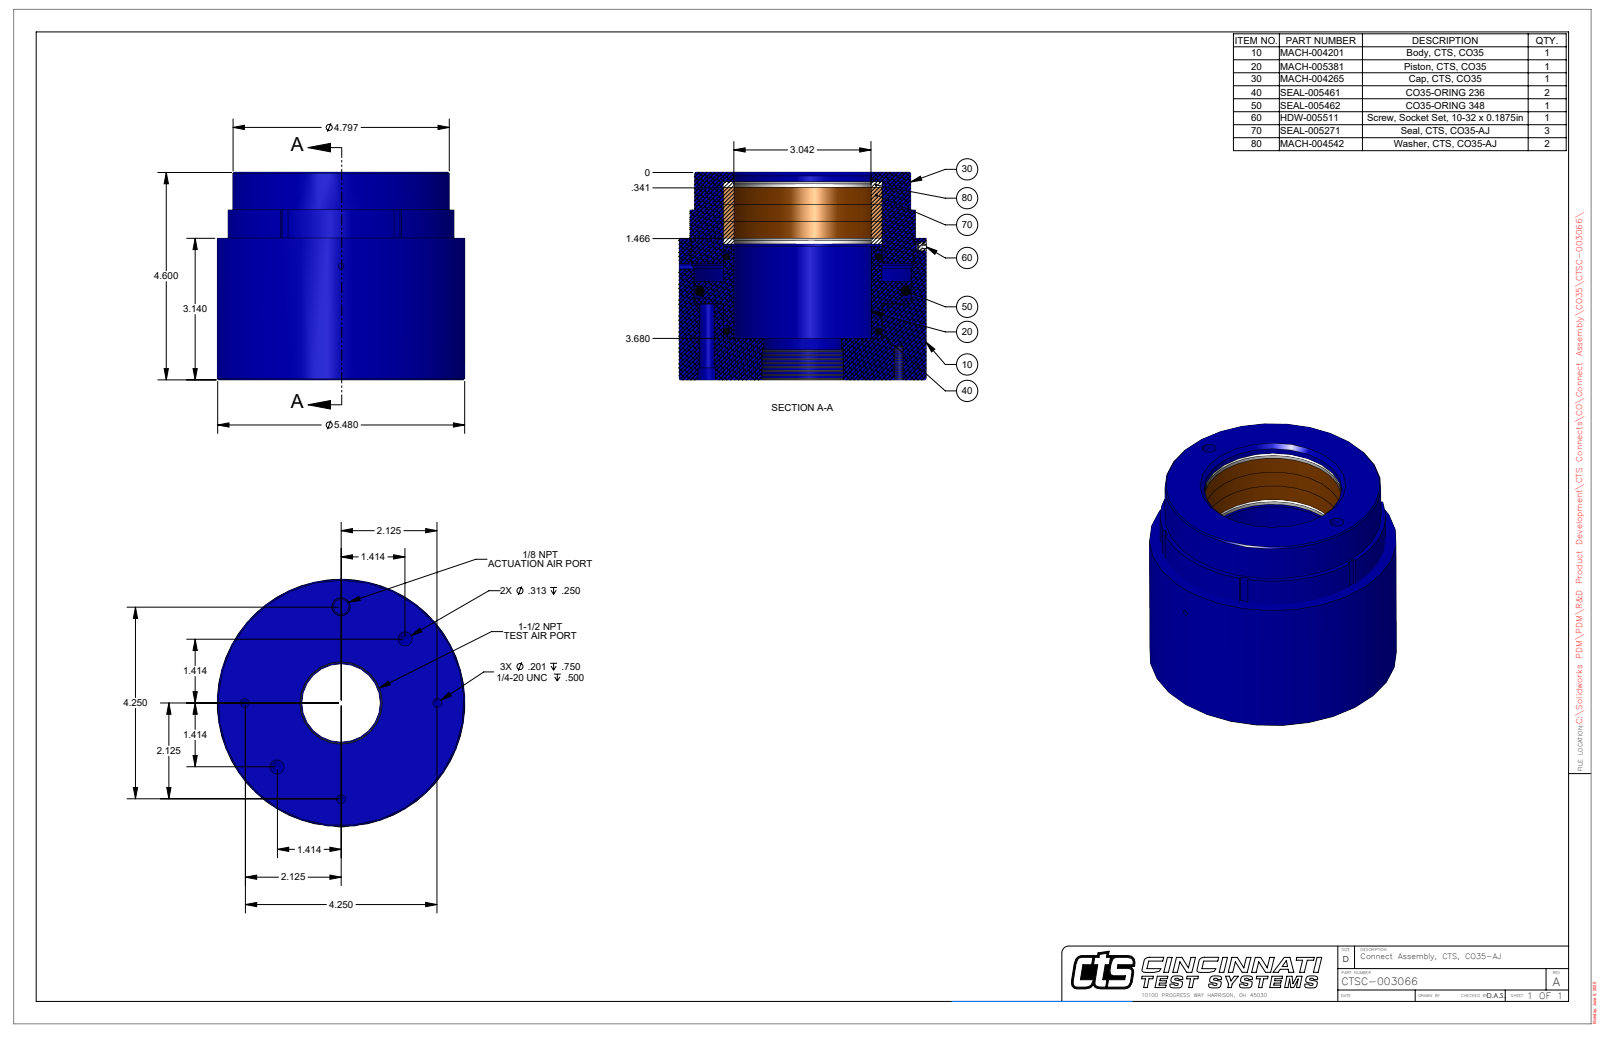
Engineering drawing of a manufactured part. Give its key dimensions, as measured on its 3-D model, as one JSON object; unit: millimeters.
{"part_name": "CTSC-003066", "step_written_by": "SolidWorks 2023 (AUTOMOTIVE_DESIGN)", "units": "millimeters", "bodies": {"solids": 2, "faces": 132, "planar": 50, "cylindrical": 58, "other": 24}, "overall_size": [139.3, 139.2, 116.8], "volume_mm3": 1178000, "surface_area_mm2": 113700, "round_holes": [[8, 4], [5.1, 3], [3.2, 1], [8.4, 1], [43.7, 1], [77.3, 1], [77.3, 1], [77.5, 1], [80.6, 1], [89.3, 1]], "round_bosses_or_shafts": [[139.2, 1], [127, 1], [121.8, 1], [89.2, 1], [89.1, 1]], "partial_cylinders_radius": [[62.5, 1], [69.2, 1]], "face_to_face_distances": [116.8, 23.4, 93.5, 108.2, 84.8, 8.7, 3.2, 111.4, 88, 5.5], "hole_center_spacings": [40.2, 50.8, 54, 74.1, 76.3, 96.8, 3.2, 38.9]}
